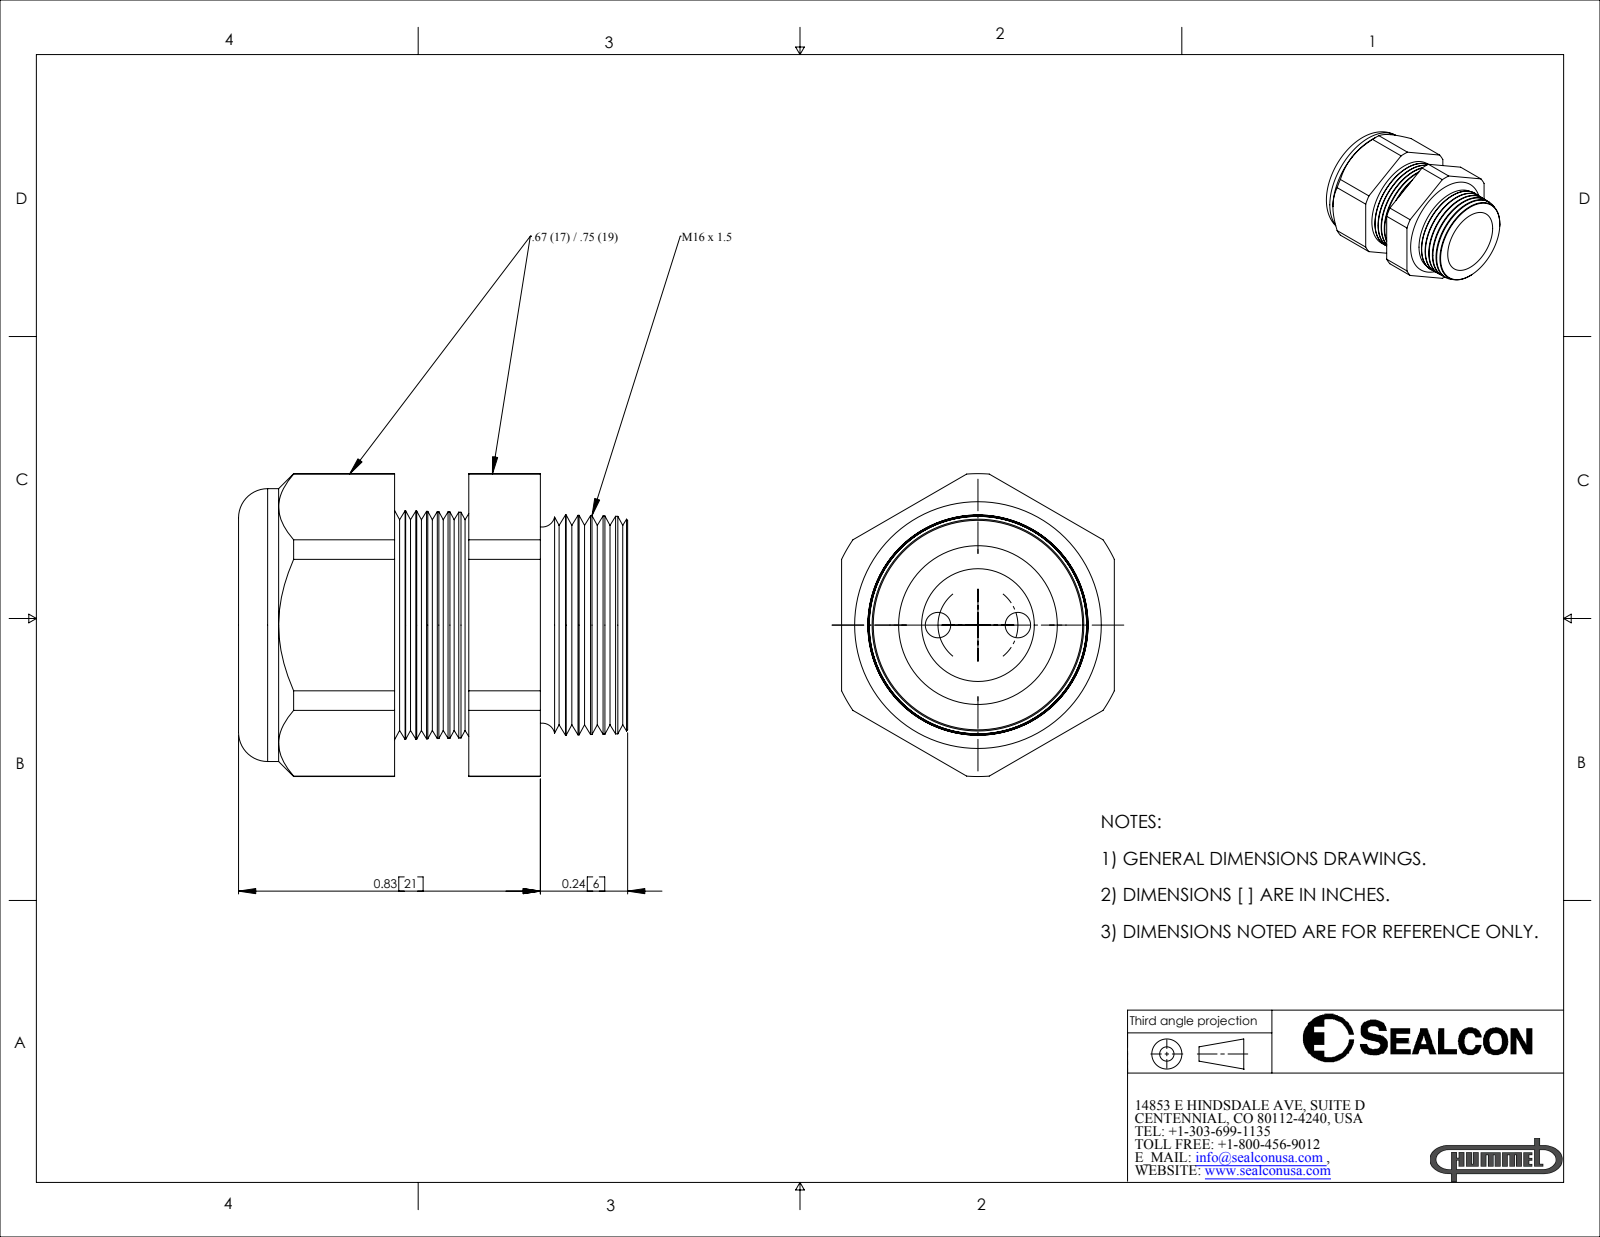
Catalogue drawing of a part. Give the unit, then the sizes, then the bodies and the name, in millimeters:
Units: millimetres
Overall size (bounding box): 27.2 × 21.2 × 19.1
Round holes (diameter × count): ⌀1.8 ×2, ⌀7.4 ×1, ⌀7.9 ×1
Round bosses / shafts (diameter × count): ⌀19.1 ×1
Partial cylindrical surfaces — rounded edges, fillets, slot ends (radius × count): R10.6 ×1
Main face-to-face distances: 19.1, 16.1, 10.9, 5.2, 21.1, 10.2, 5, 27.2, 16.3, 11.1
Hole centre spacings: 2.8, 5.6
Volume: 5 210 mm³ · Surface area: 3 680 mm²
Bodies: 2 solids, 136 faces (20 planar, 24 cylindrical, 92 other)
Part name (STEP PRODUCT): CD16M4-BR
STEP written by: SolidWorks 2007 (CONFIG_CONTROL_DESIGN)
